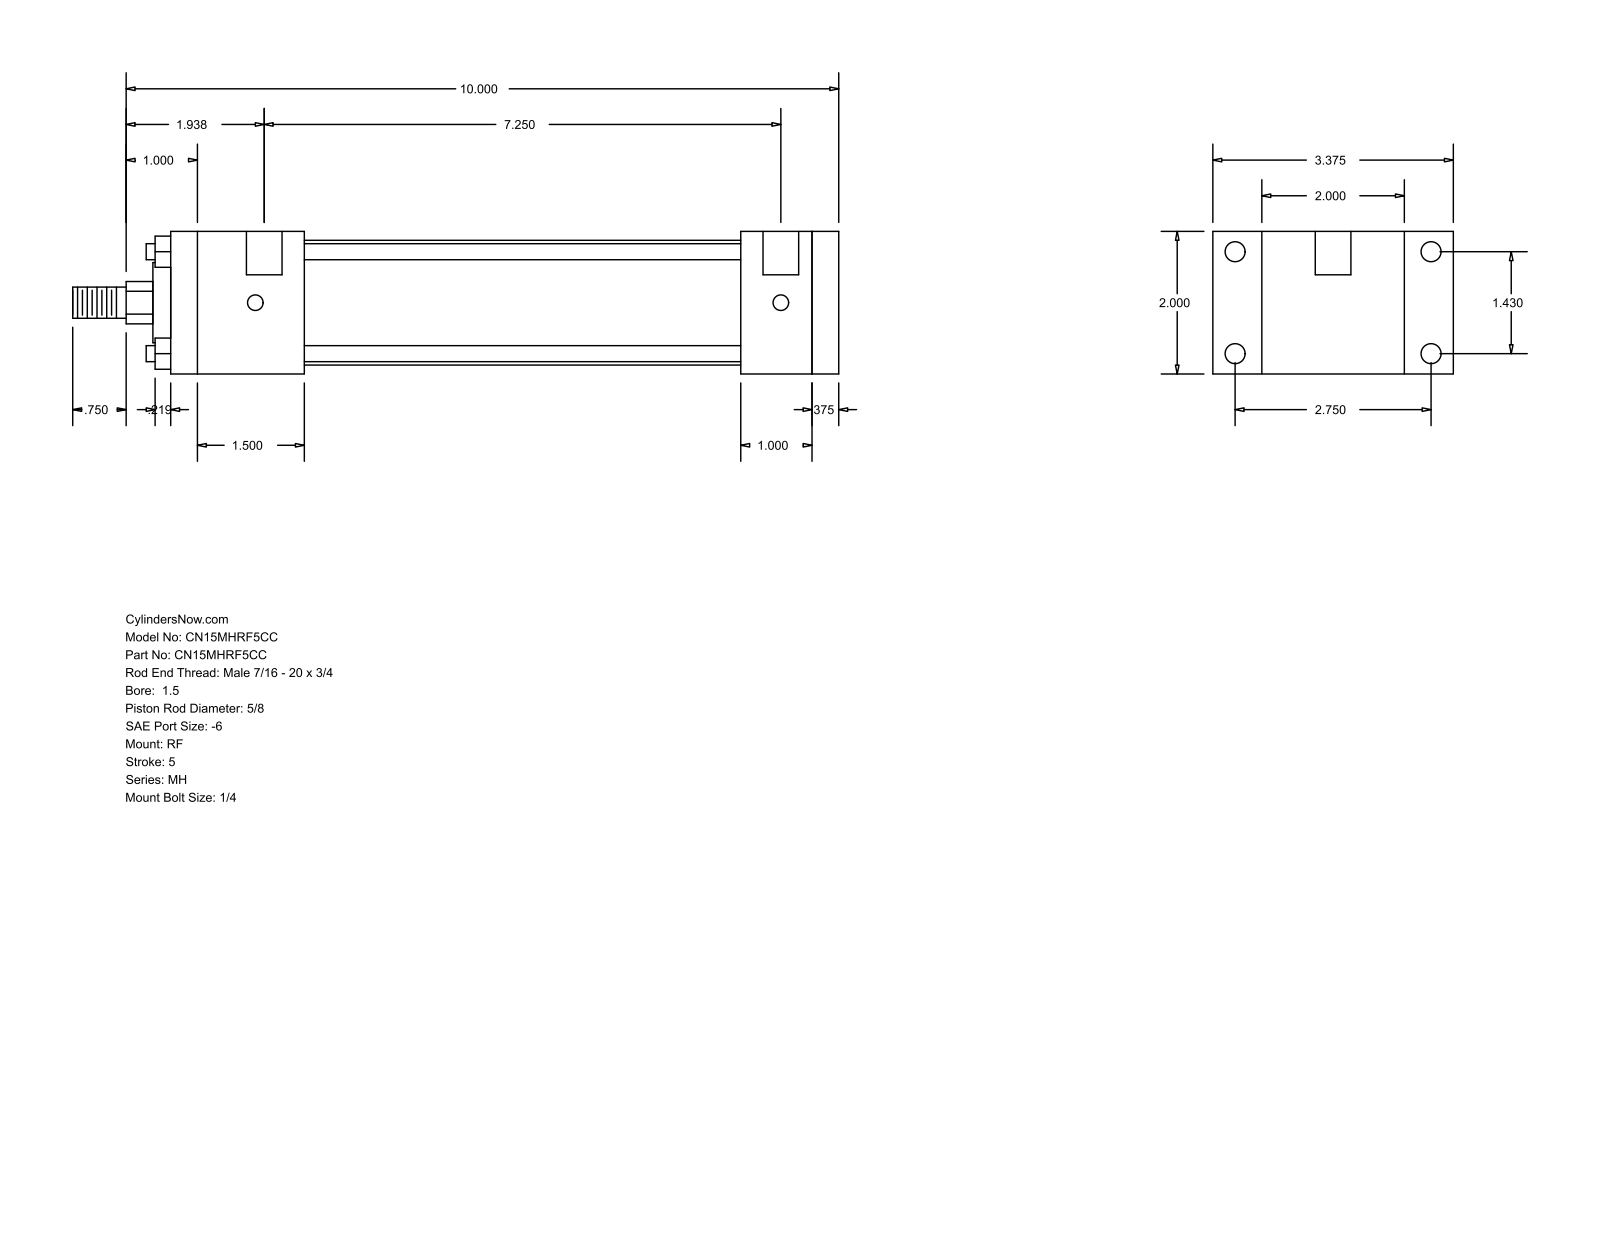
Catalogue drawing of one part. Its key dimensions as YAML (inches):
part_name: "MH_RF__0150_0.625"
step_written_by: "GSSL Pune (CONFIG_CONTROL_DESIGN)"
units: inches
bodies: {solids: 0, faces: 92, planar: 64, cylindrical: 28, other: 0}
overall_size: [10.75, 3.375, 2]
round_holes:
  - {diameter: 0.219, count: 4}
  - {diameter: 0.281, count: 4}
  - {diameter: 0.5, count: 2}
round_bosses_or_shafts:
  - {diameter: 0.225, count: 4}
  - {diameter: 1.75, count: 1}
  - {diameter: 1.125, count: 1}
  - {diameter: 0.625, count: 1}
  - {diameter: 0.437, count: 1}
partial_cylinders:
  - {radius: 0.297, count: 1}
face_to_face_distances: [2, 0.375, 9.375, 9, 1.375, 1, 0.687, 2.687, 8, 1.875]
hole_center_spacings: [1.43, 2.75, 3.099, 7.375, 0.125, 7.25]
